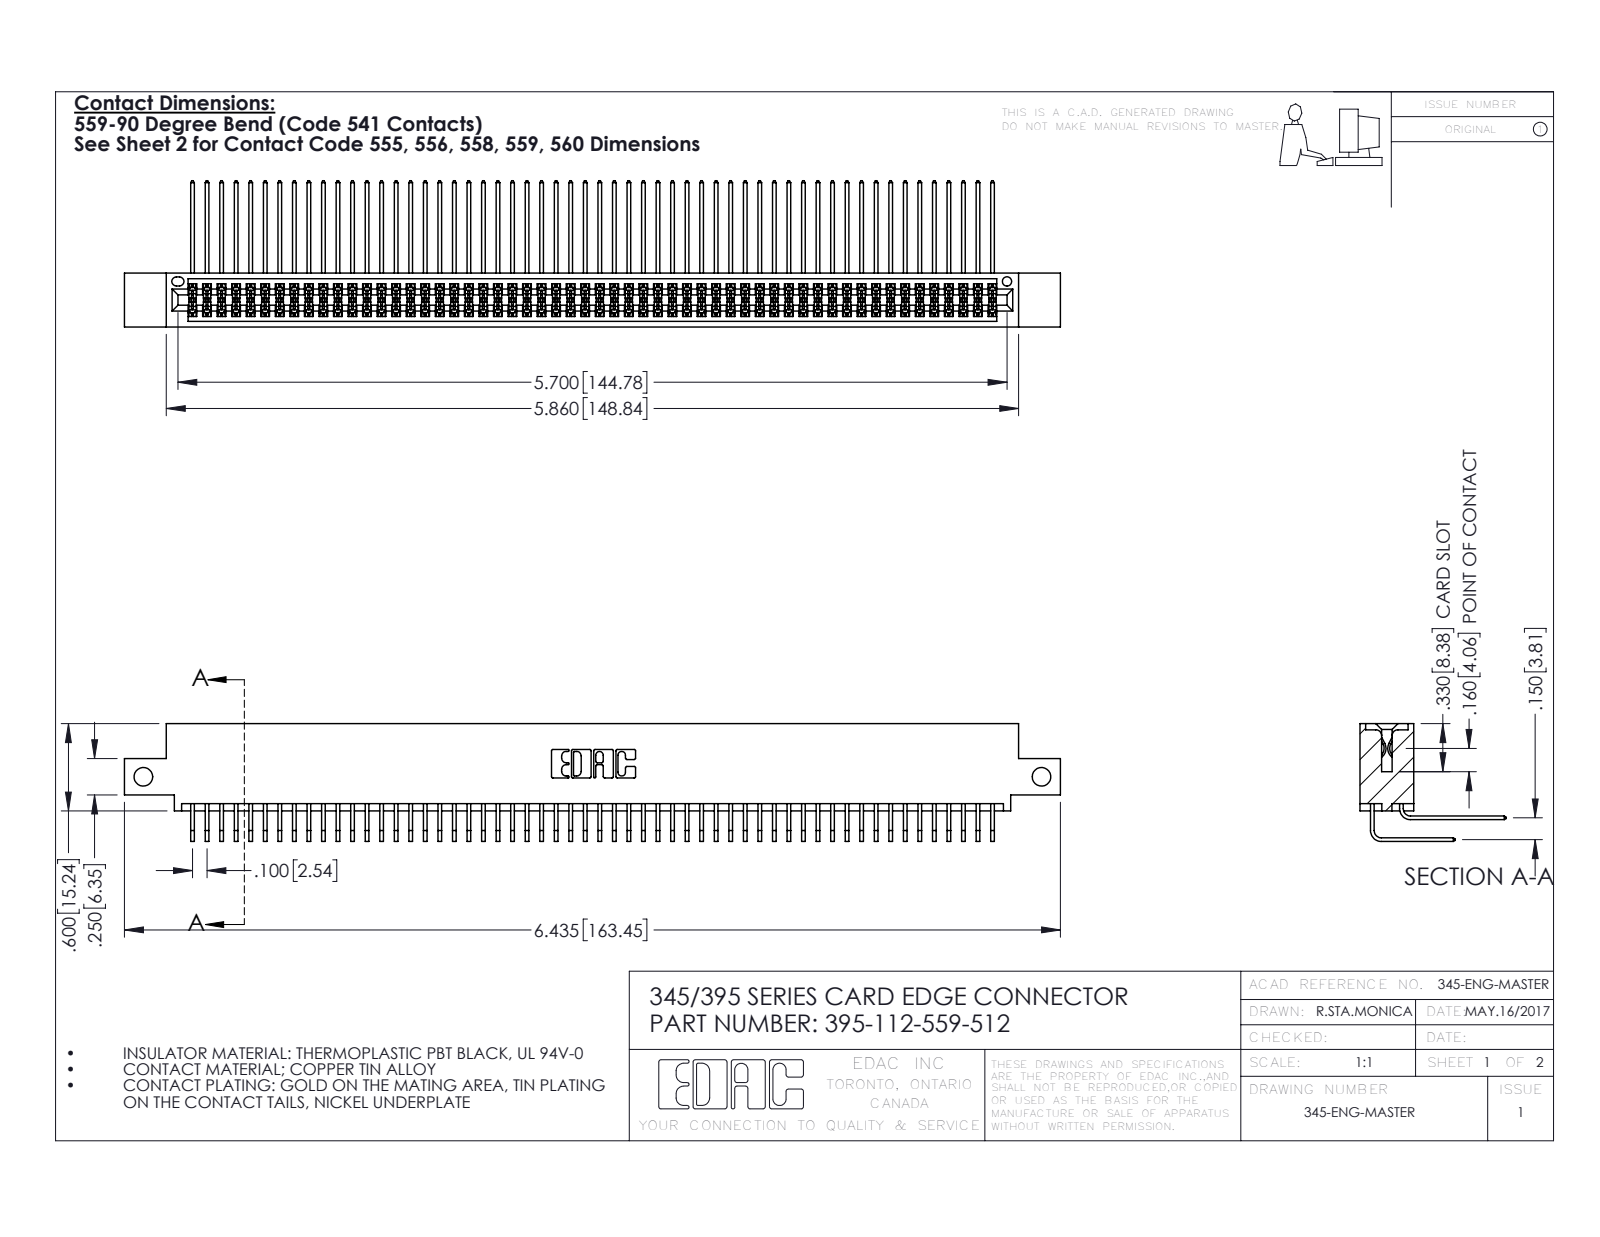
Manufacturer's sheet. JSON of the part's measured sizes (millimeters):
{"part_name": "345-292-001_559 Tail - 2; 395-112-559-512; 345 Part_0.110 Offset - Side Mount; 345-292-001_558 559 Tail - 1", "step_written_by": "SolidWorks 2016 (CONFIG_CONTROL_DESIGN)", "units": "millimeters", "bodies": {"solids": 113, "faces": 5954, "planar": 4004, "cylindrical": 1950, "other": 0}, "overall_size": [163.4, 25.5, 20.5], "volume_mm3": 16490, "surface_area_mm2": 27650, "round_holes": [[3.3, 2], [1.6, 1]], "partial_cylinders_radius": [[0.2, 169], [0.3, 22], [0.2, 6], [0.8, 6], [0.7, 3], [0.4, 2], [0.5, 2], [0.6, 2]], "face_to_face_distances": [1.8, 7.6, 5.1, 9.4, 2.5, 6.9, 0.6, 5.7, 4.4, 3.8], "hole_center_spacings": [156.8]}
